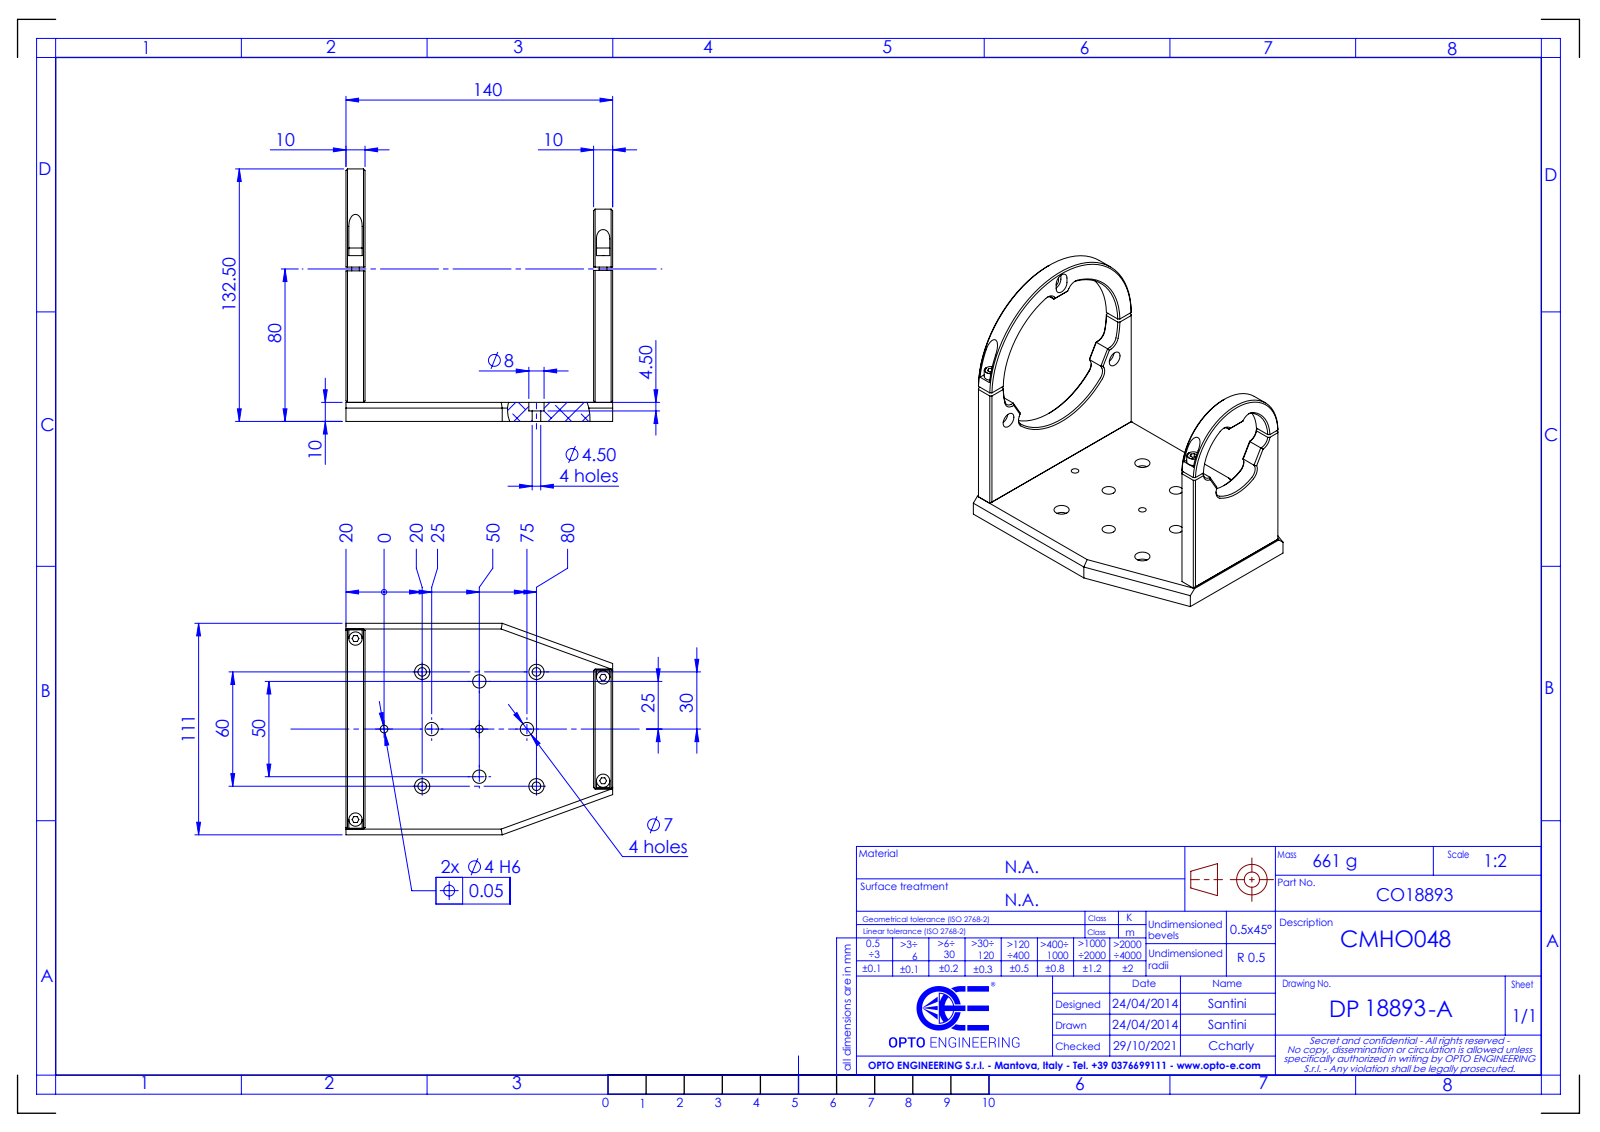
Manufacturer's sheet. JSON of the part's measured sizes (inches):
{"part_name": "DP18893-A_CMHO048", "step_written_by": "SolidWorks 2021 (CONFIG_CONTROL_DESIGN)", "units": "inches", "bodies": {"solids": 0, "faces": 319, "planar": 161, "cylindrical": 94, "other": 64}, "overall_size": [5.512, 5.217, 4.37], "round_holes": [[0.315, 10], [0.177, 6], [0.276, 6], [0.157, 2]], "round_bosses_or_shafts": [[0.276, 4], [0.157, 2]], "partial_cylinders_radius": [[0.197, 12], [0.089, 2], [0.157, 2], [0.941, 1], [1.236, 1], [1.673, 1], [2.067, 1]], "face_to_face_distances": [0.394, 5.118, 5.512, 4.724, 0.118, 0.831, 3.303, 0.949, 3.421, 4.252], "hole_center_spacings": [1.197, 2.467, 1.392, 0.984, 1.67, 1.969, 2.362, 1.409]}
